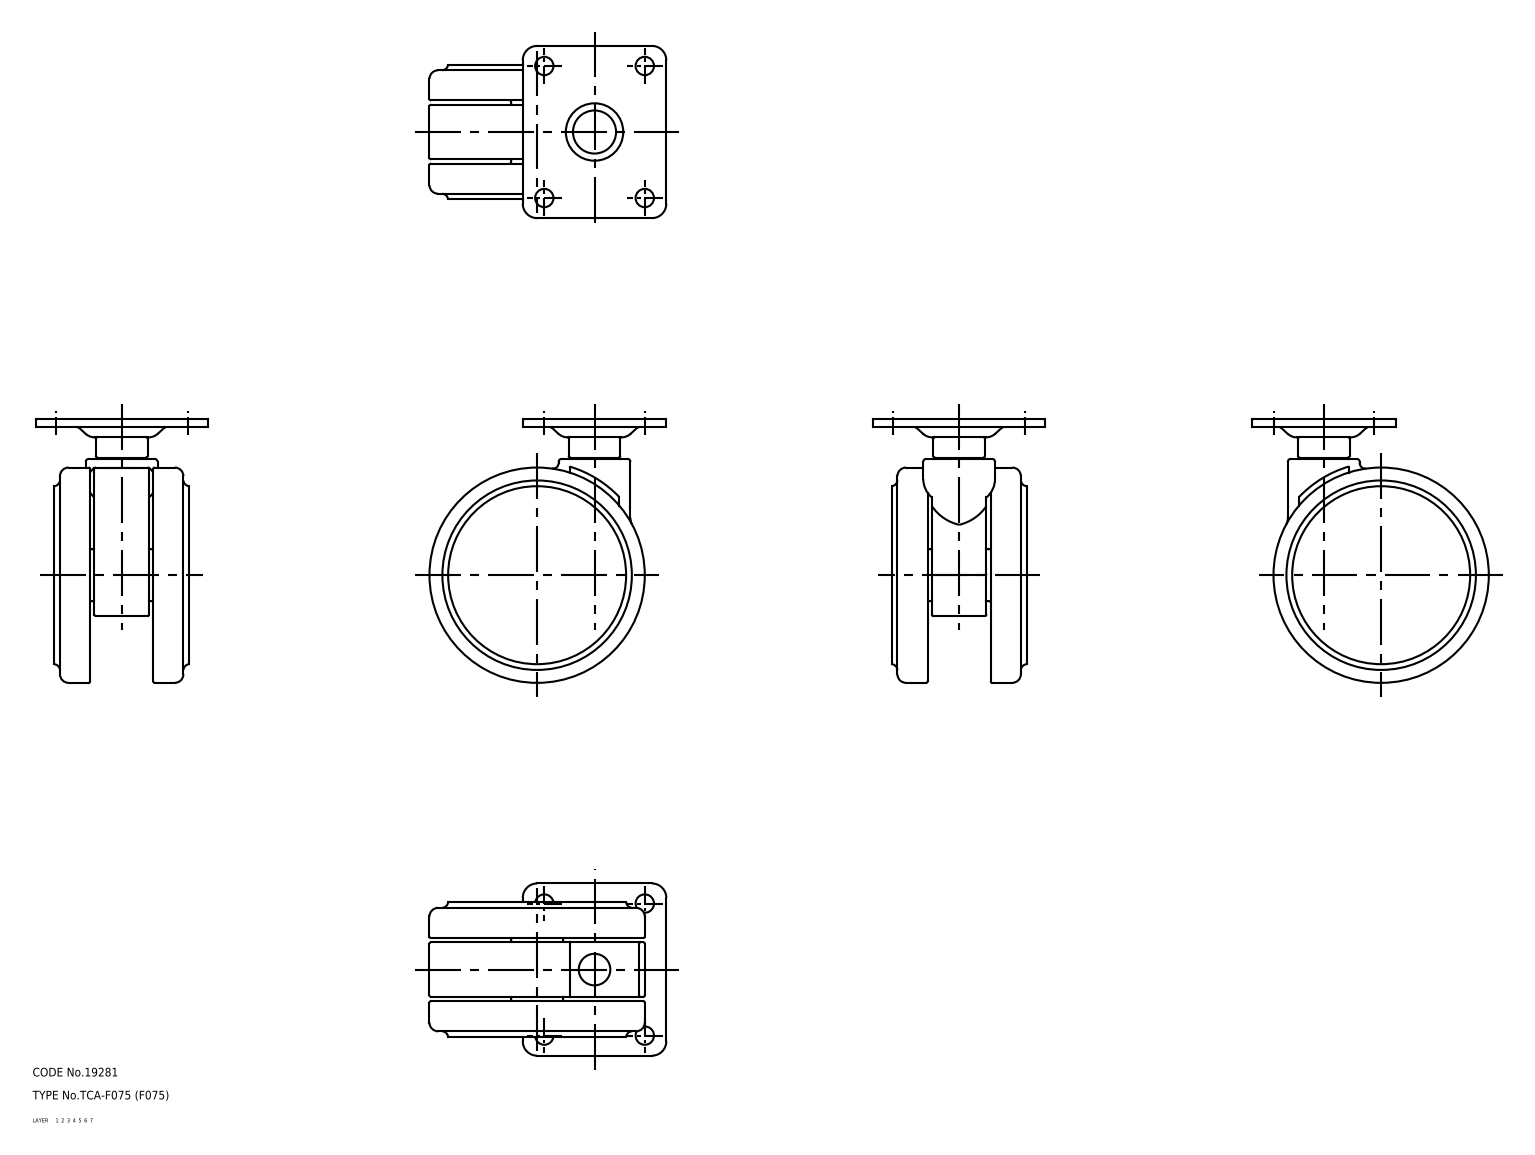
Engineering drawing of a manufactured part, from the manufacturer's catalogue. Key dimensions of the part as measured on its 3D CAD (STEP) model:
Part name (STEP PRODUCT): 67118387; 67118400; 67118413; 67118426 (+1 more)
STEP written by: CADfix (AUTOMOTIVE_DESIGN)
Units: millimetres
Bodies: 5 solids, 140 faces (0 planar, 0 cylindrical, 140 other)
Overall size (bounding box): 92 × 82.5 × 60
Volume: 168 463 mm³ · Surface area: 43 398 mm²
